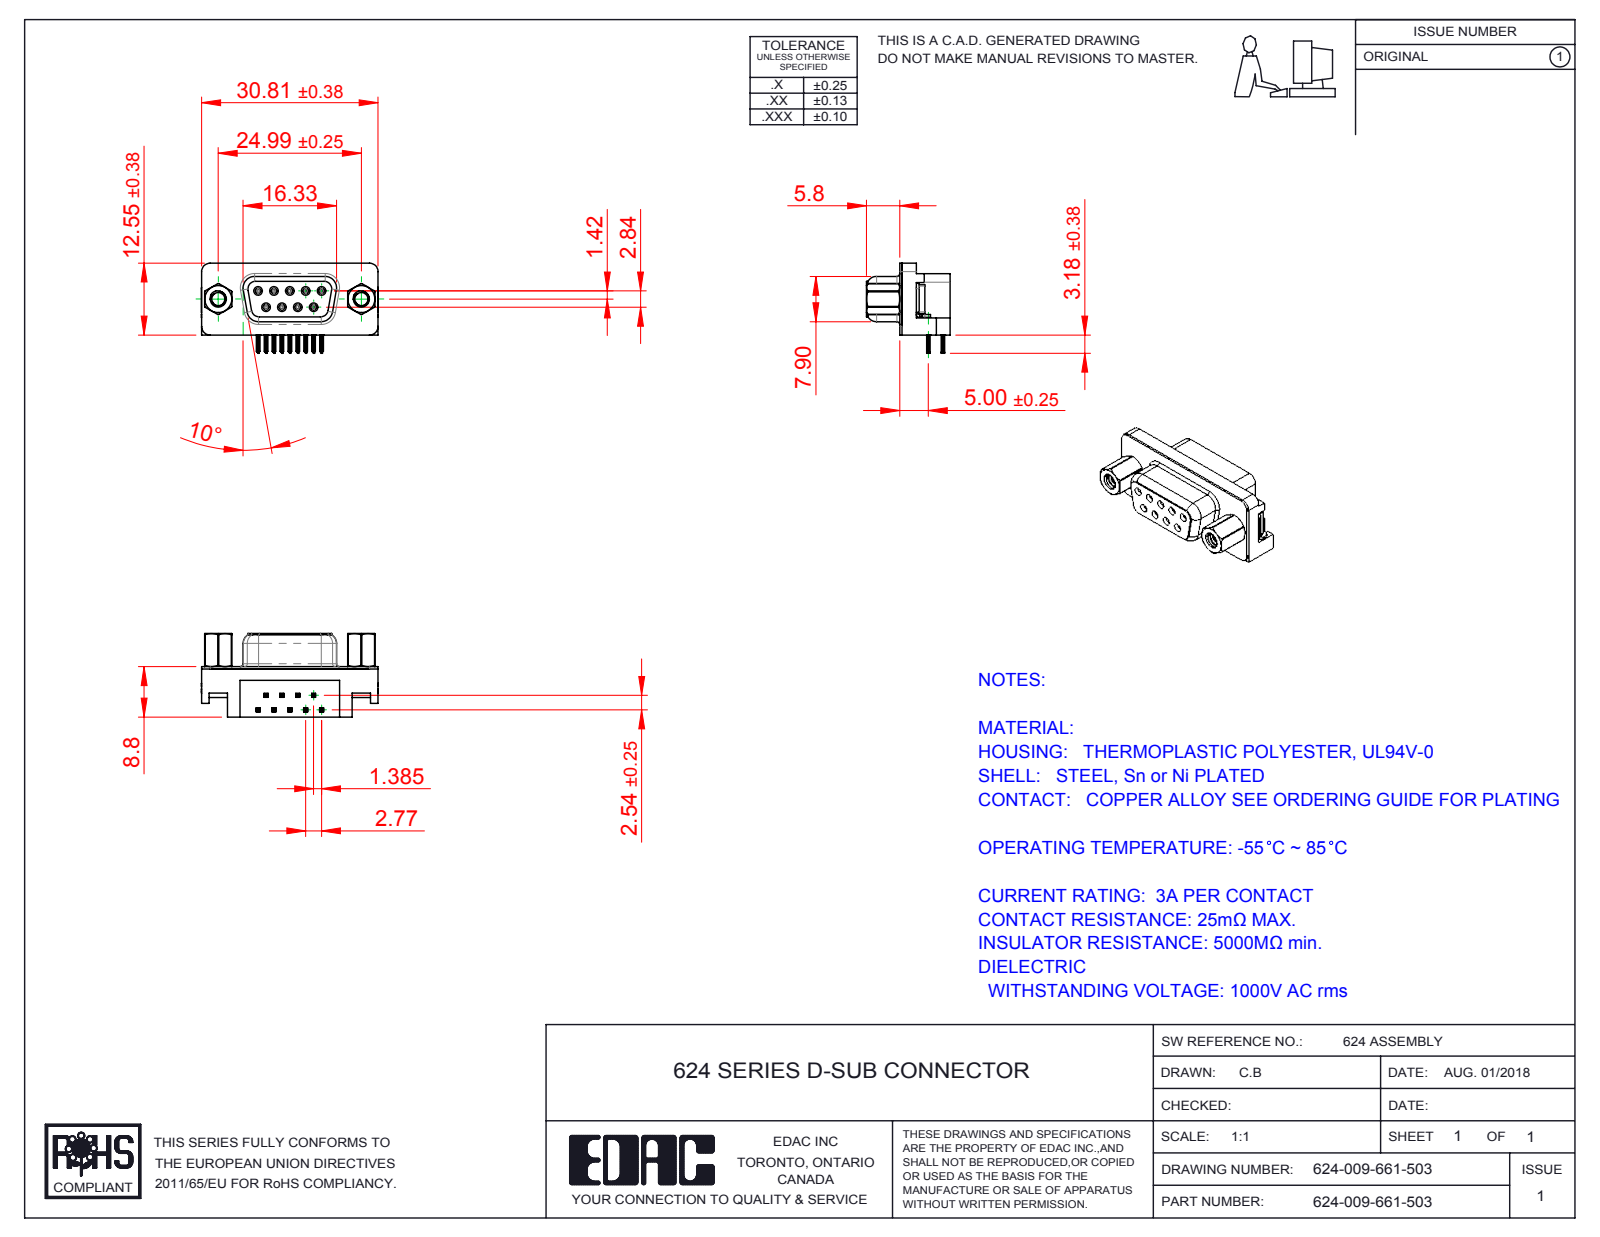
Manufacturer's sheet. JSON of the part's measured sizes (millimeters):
{"part_name": "624 4-40 Threaded Rivet; 624 Non Board Mount; 624 Contact Top; 624 Socket Bottom (+4 more)", "step_written_by": "SolidWorks 2016 (CONFIG_CONTROL_DESIGN)", "units": "millimeters", "bodies": {"solids": 17, "faces": 1644, "planar": 664, "cylindrical": 474, "other": 506}, "overall_size": [30.89, 15.73, 14.6], "volume_mm3": 3146, "surface_area_mm2": 4805, "round_holes": [[0.8, 9], [0.9, 9], [2.26, 2], [2.29, 2], [4, 2], [4.8, 2], [5, 2]], "round_bosses_or_shafts": [[1.2, 9], [4.9, 2], [4.75, 2], [3.9, 2], [2.79, 2]], "partial_cylinders_radius": [[0.1, 72], [0.15, 36], [0.35, 18], [1, 18], [0.34, 9], [0.25, 8], [1.35, 8], [1.5, 7]], "face_to_face_distances": [0.4, 8.4, 8.8, 2.9, 6.2, 2.5, 5.9, 0.35, 5.8, 10.69], "hole_center_spacings": [3.16, 2.77, 5.54, 5.03, 5.04, 8.31, 7.48, 7.49]}
